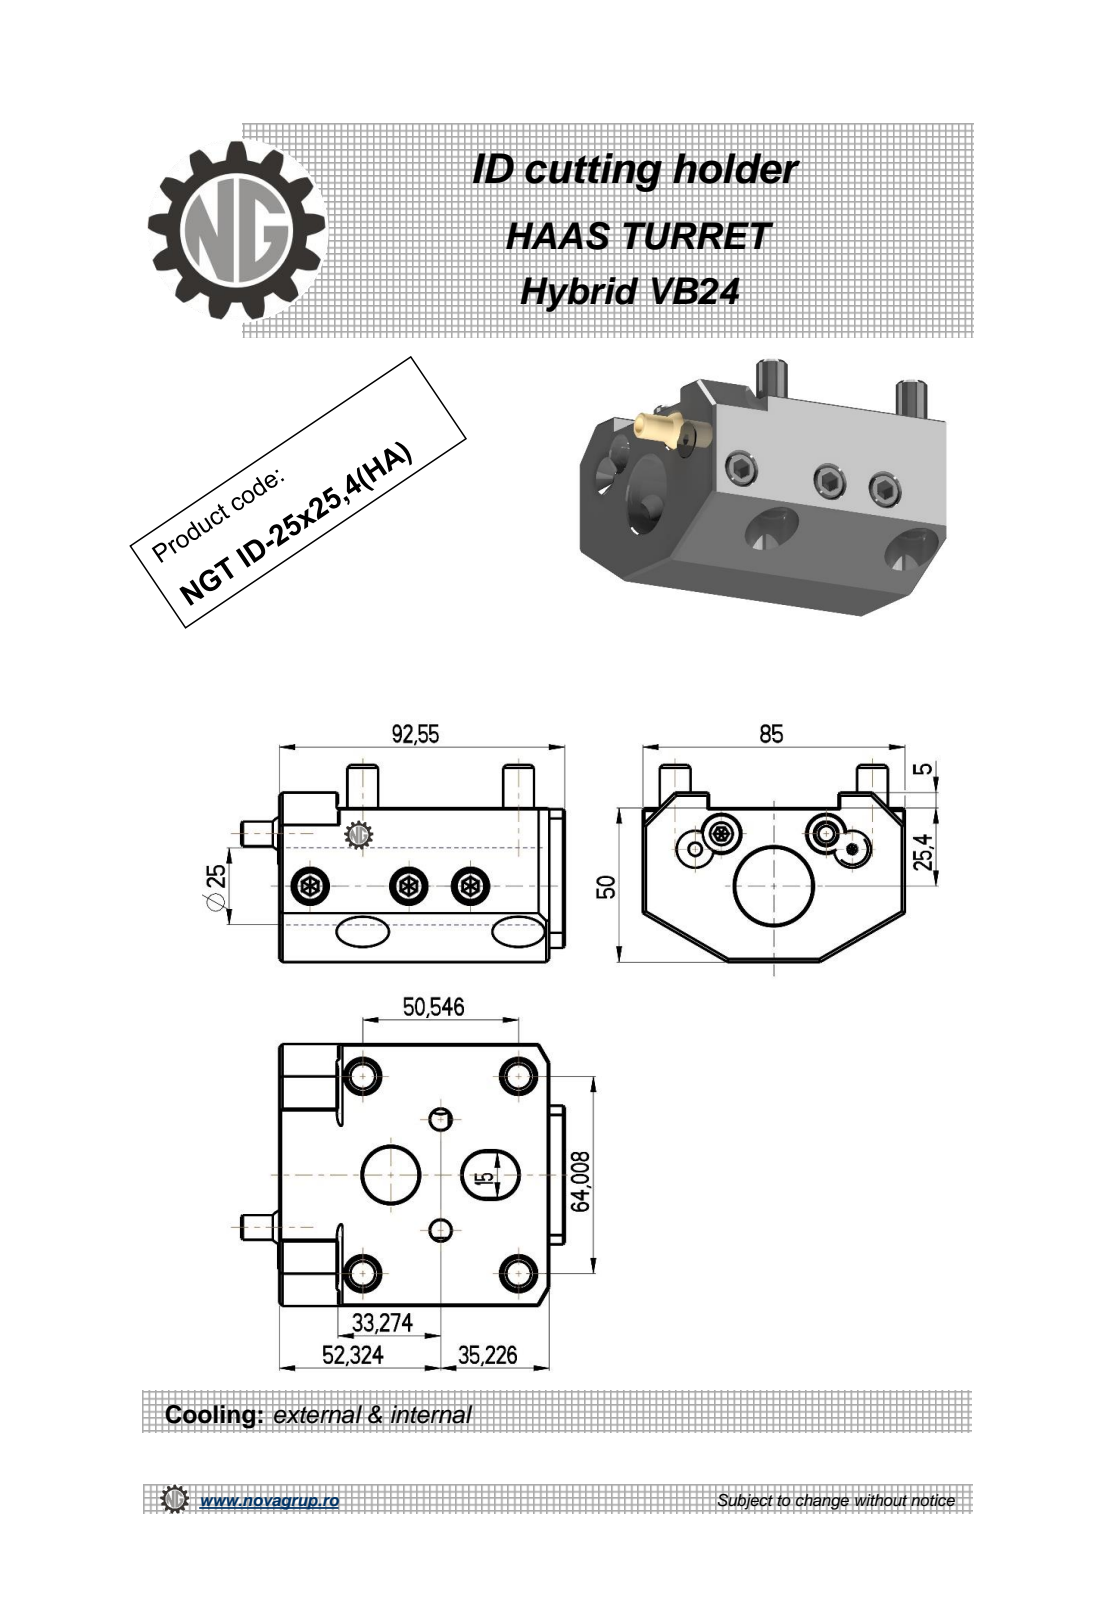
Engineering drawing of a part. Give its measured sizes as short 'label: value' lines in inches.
name: NGT_ID_25_25_4_HA
written by: PRO/ENGINEER BY PARAMETRIC TECHNOLOGY CORPORATION, 2010280 (CONFIG_CONTROL_DESIGN)
unit: in
bodies: 1 solid, 339 faces (137 planar, 101 cylindrical, 101 other)
size: 4.13 × 3.346 × 2.52
volume: 18.21 in³; area: 70.87 in²
holes: 3× ⌀0.335, 3× ⌀0.433, 2× ⌀0.268, 1× ⌀0.197, 1× ⌀0.709, 1× ⌀0.984
bosses: 8× ⌀0.394, 1× ⌀0.315
rounds: 36× R0.02, 6× R0.008, 2× R0.295
face distances: 0.197, 1.969, 3.346, 3.644, 3.447, 1.772, 0.787, 2.559, 0.394, 2.165
hole spacings: 0.953, 0.787, 0.946, 1.26, 1.417, 2.047
